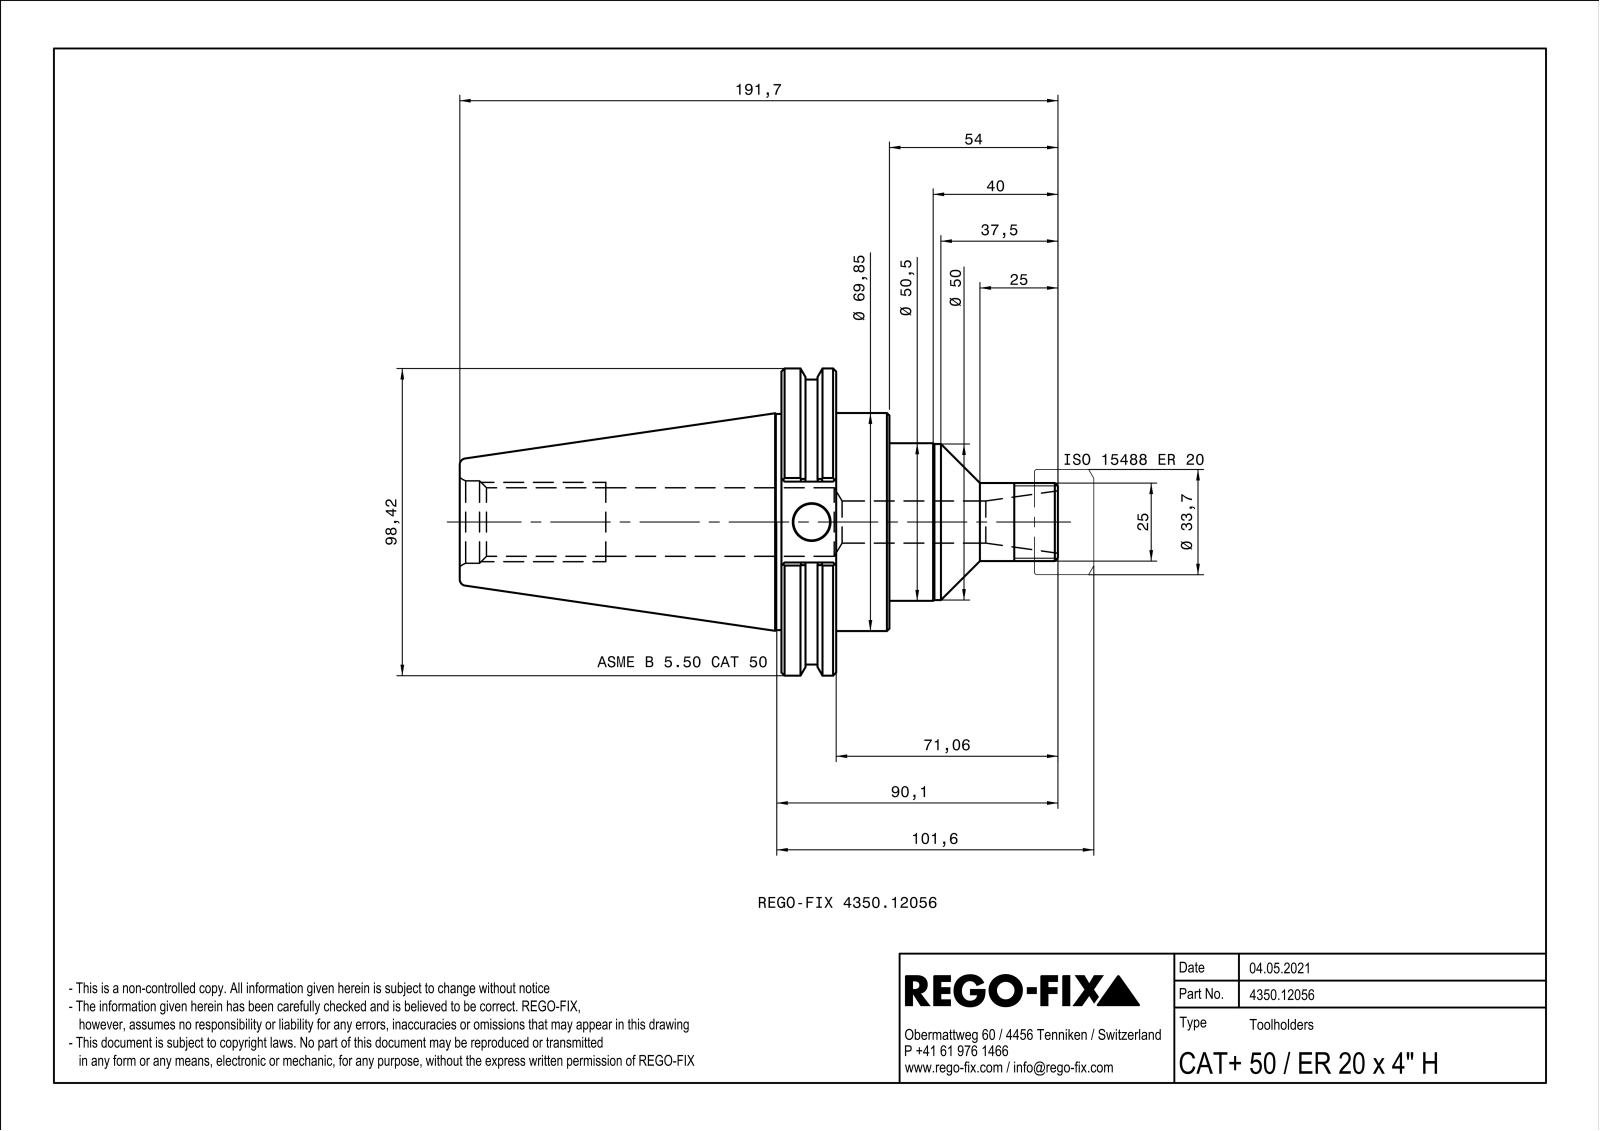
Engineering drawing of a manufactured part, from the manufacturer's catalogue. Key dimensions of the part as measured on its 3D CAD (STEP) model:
Part name (STEP PRODUCT): NOCUT
STEP written by: SIEMENS PLM Software Solid Edge ST10 (AUTOMOTIVE_DESIGN)
Units: millimetres
Bodies: 2 solids, 249 faces (102 planar, 59 cylindrical, 88 other)
Overall size (bounding box): 192.1 × 98.72 × 94.65
Volume: 863 765 mm³ · Surface area: 115 149 mm²
Round holes (diameter × count): ⌀3.9 ×2, ⌀4.5 ×2, ⌀3.24 ×1, ⌀12 ×1, ⌀13.5 ×1, ⌀21.96 ×1, ⌀26.1 ×1, ⌀26.4 ×1
Round bosses / shafts (diameter × count): ⌀98.72 ×1, ⌀98.43 ×1, ⌀91.3 ×1, ⌀70.15 ×1, ⌀69.85 ×1, ⌀69.25 ×1, ⌀50.8 ×1, ⌀50.5 ×1
Partial cylindrical surfaces — rounded edges, fillets, slot ends (radius × count): R0.5 ×4
Main face-to-face distances: 33.75, 17.55, 17.75, 16, 33.55, 16.2, 33.95, 136.85, 103.1, 72.73
